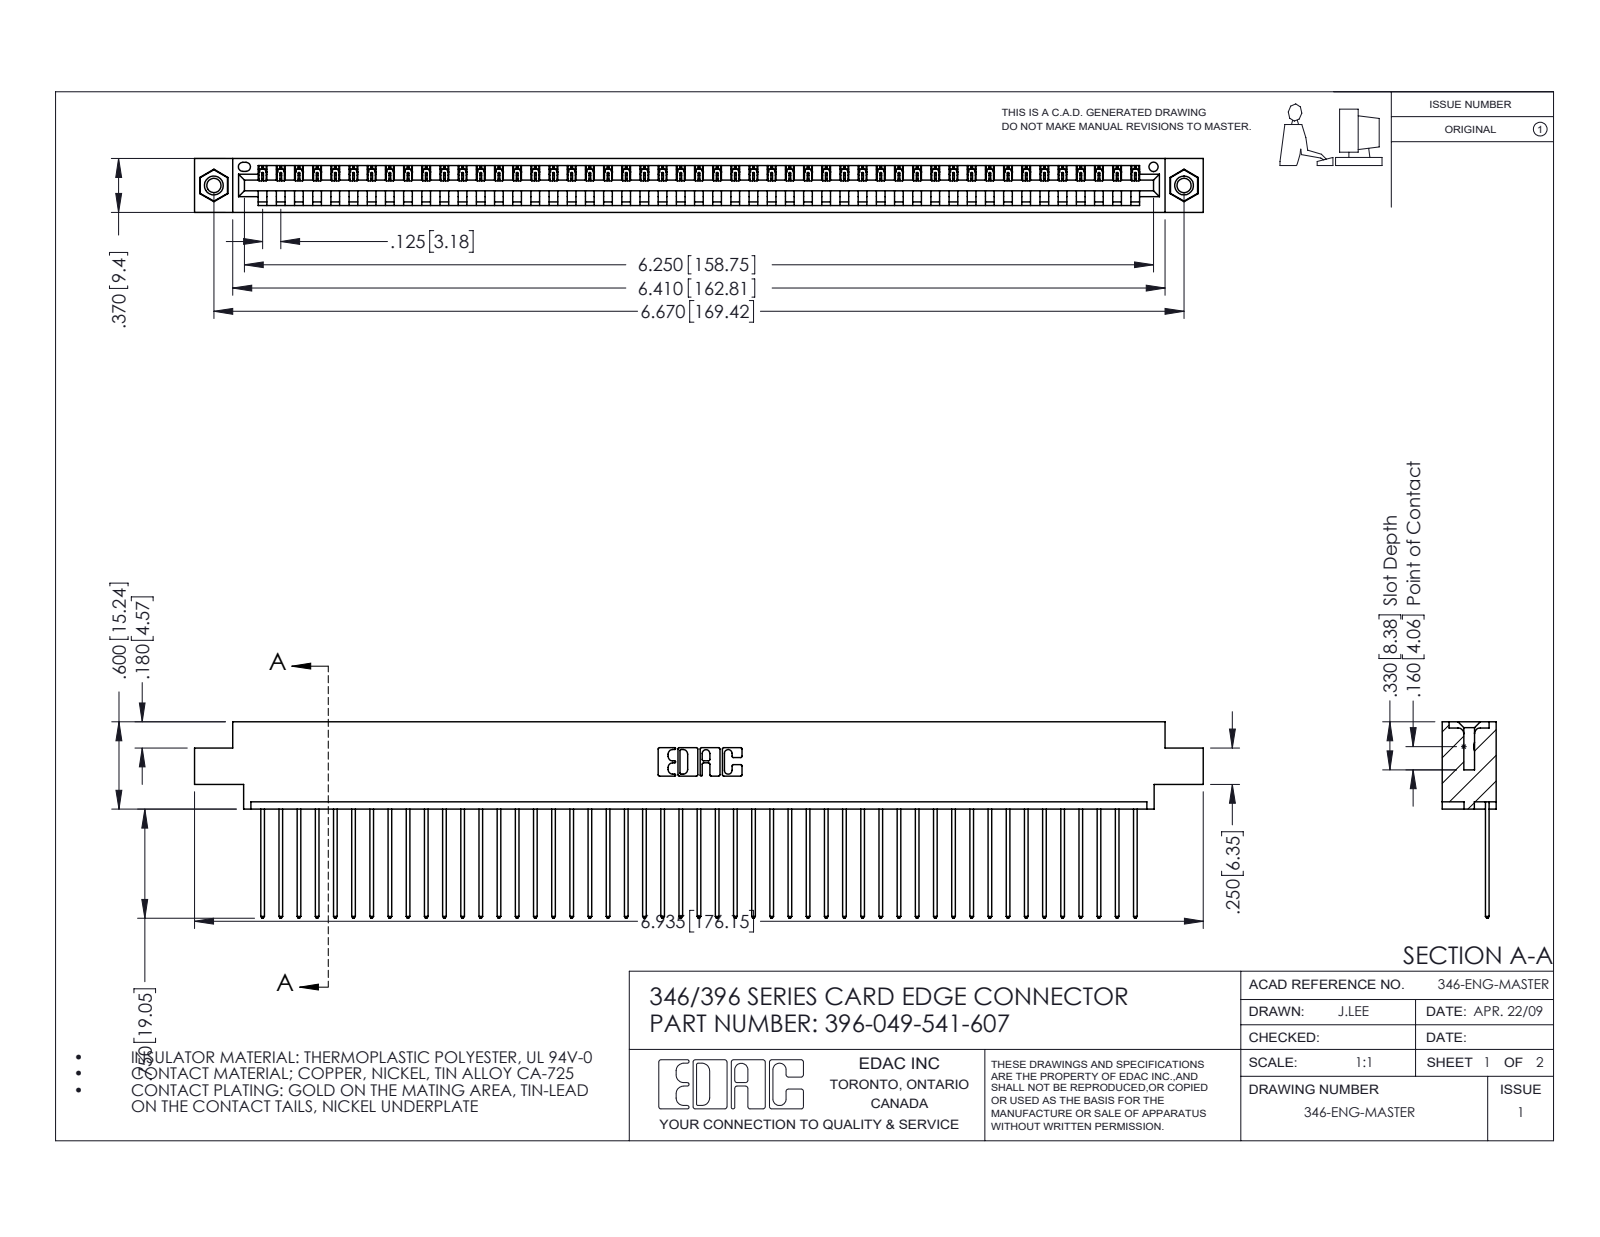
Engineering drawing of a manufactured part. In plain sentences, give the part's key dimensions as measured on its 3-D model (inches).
The part is named "345-292-001_345-293-141; 346 Part_0.170 Offset - 0.156 Dia-TI; 345-250-001_345-250-005-103; 396-049-541-607". Its 3-D file was written by "SolidWorks 2016 (CONFIG_CONTROL_DESIGN)". It is 52 solids with 3028 faces: 2072 planar, 940 cylindrical and 16 other. Overall it measures 6.935 by 1.35 by 0.37 inches. Its volume is 1.031 cubic inches and its surface area 34.66 square inches. Round holes: 2 of diameter 0.098, 2 of diameter 0.125, 2 of diameter 0.156, 1 of diameter 0.064. Round bosses or shafts: 2 of diameter 0.155. Partial cylindrical surfaces (rounded edges, fillets, slot ends): 98 of radius 0.006, 98 of radius 0.01, 22 of radius 0.01, 6 of radius 0.007, 6 of radius 0.031, 3 of radius 0.026, 2 of radius 0.031, 2 of radius 0.04. The main face-to-face distances are 0.048, 0.322, 0.37, 0.25, 0.072, 0.298, 0.025, 0.222, 0.148, 0.1. The hole center spacings are 0.246, 6.461, 6.67.
